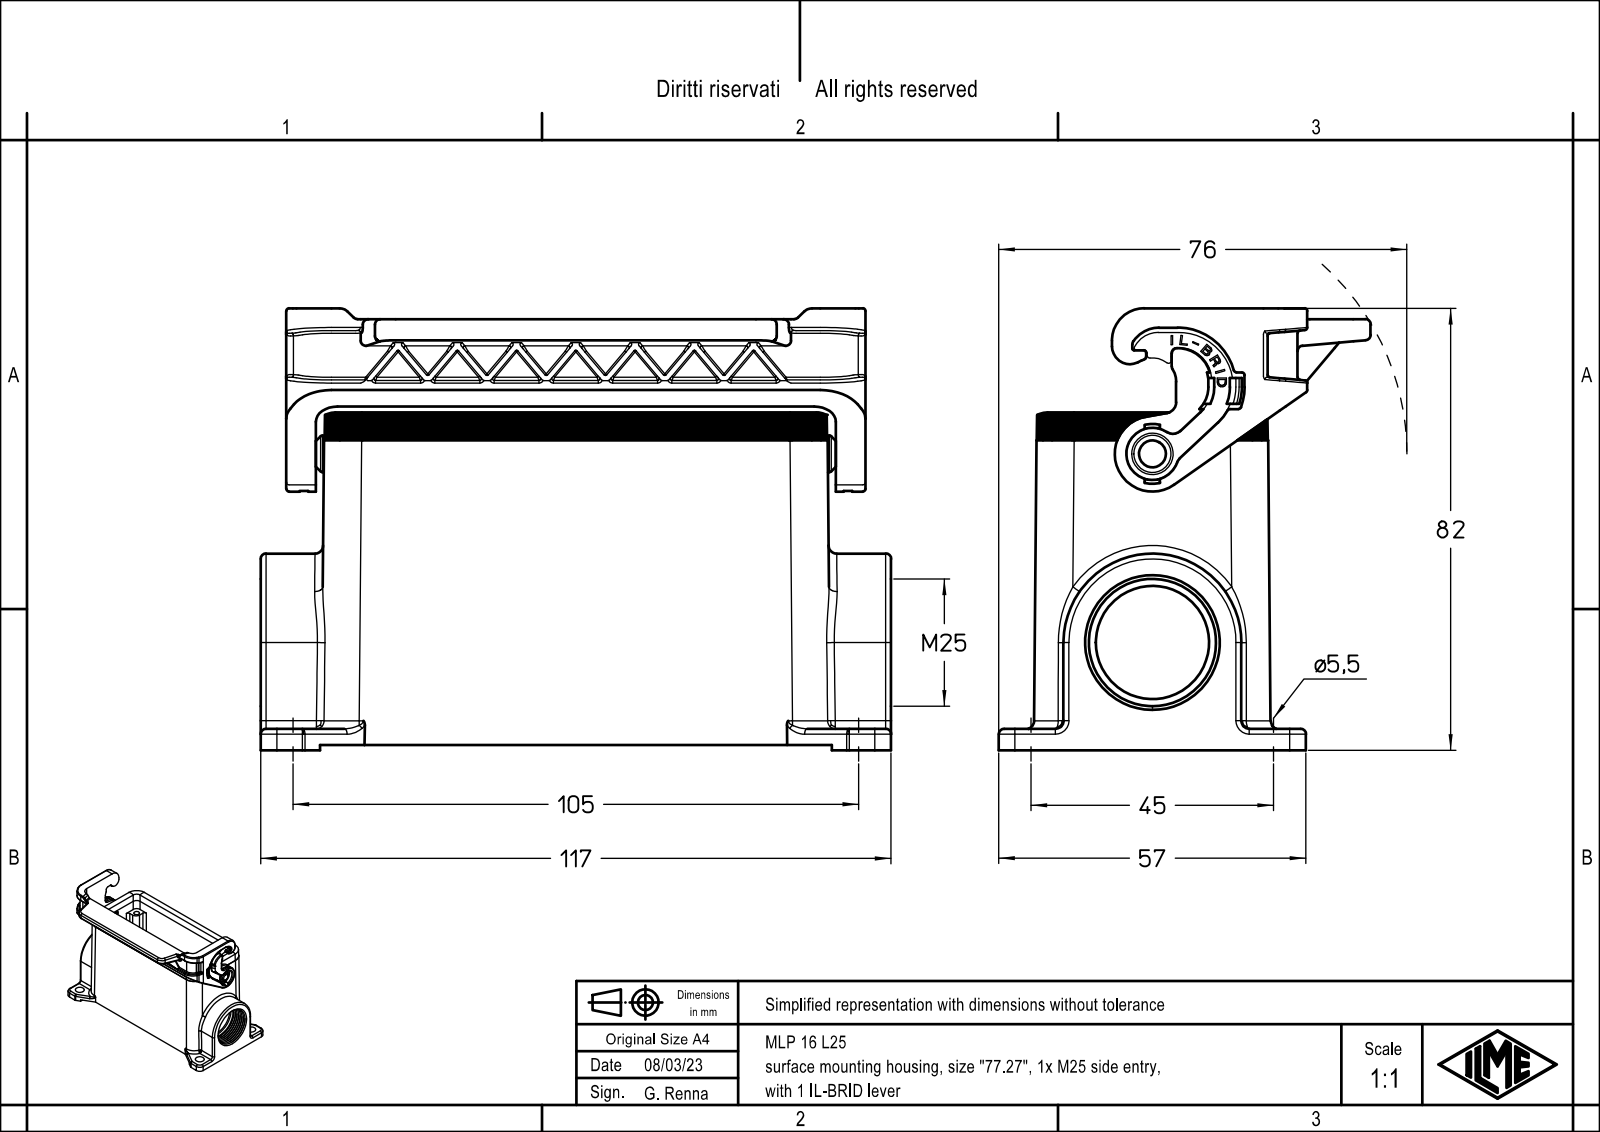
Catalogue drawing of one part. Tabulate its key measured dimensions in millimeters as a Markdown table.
| quantity | value |
| --- | --- |
| part name | MLP 16 L25 |
| STEP written by | Creo Elements/Direct Modeling 20.1B 02-Apr-2019 (C) Parametric Technology GmbH (AUTOMOTIVE_DESIGN) |
| units | millimeters |
| bodies | 1 solid, 1075 faces (636 planar, 293 cylindrical, 146 other) |
| overall size | 117 × 82 × 69 |
| volume | 114 686 mm³ |
| surface area | 59 878 mm² |
| round holes (diameter × count) | 3 × 4, 3.5 × 4, 5.5 × 4, 3.25 × 1, 5.4 × 1, 7.7 × 1, 21 × 1, 23.6 × 1 |
| round bosses / shafts (diameter × count) | 6.9 × 1, 6.8 × 1, 5.2 × 1, 3.2 × 1 |
| partial cylindrical surfaces (radius × count) | 0.1 × 27, 1 × 19, 3 × 16, 0.2 × 15, 1.5 × 13, 0.5 × 11, 7 × 10, 2 × 9 |
| main face-to-face distances | 3, 10.25, 106.75, 1, 79, 76, 4, 4.75, 5.5, 112.25 |
| hole center spacings | 16.43, 38.54, 91.69, 98.09, 27, 45, 77.5, 82.07 |
